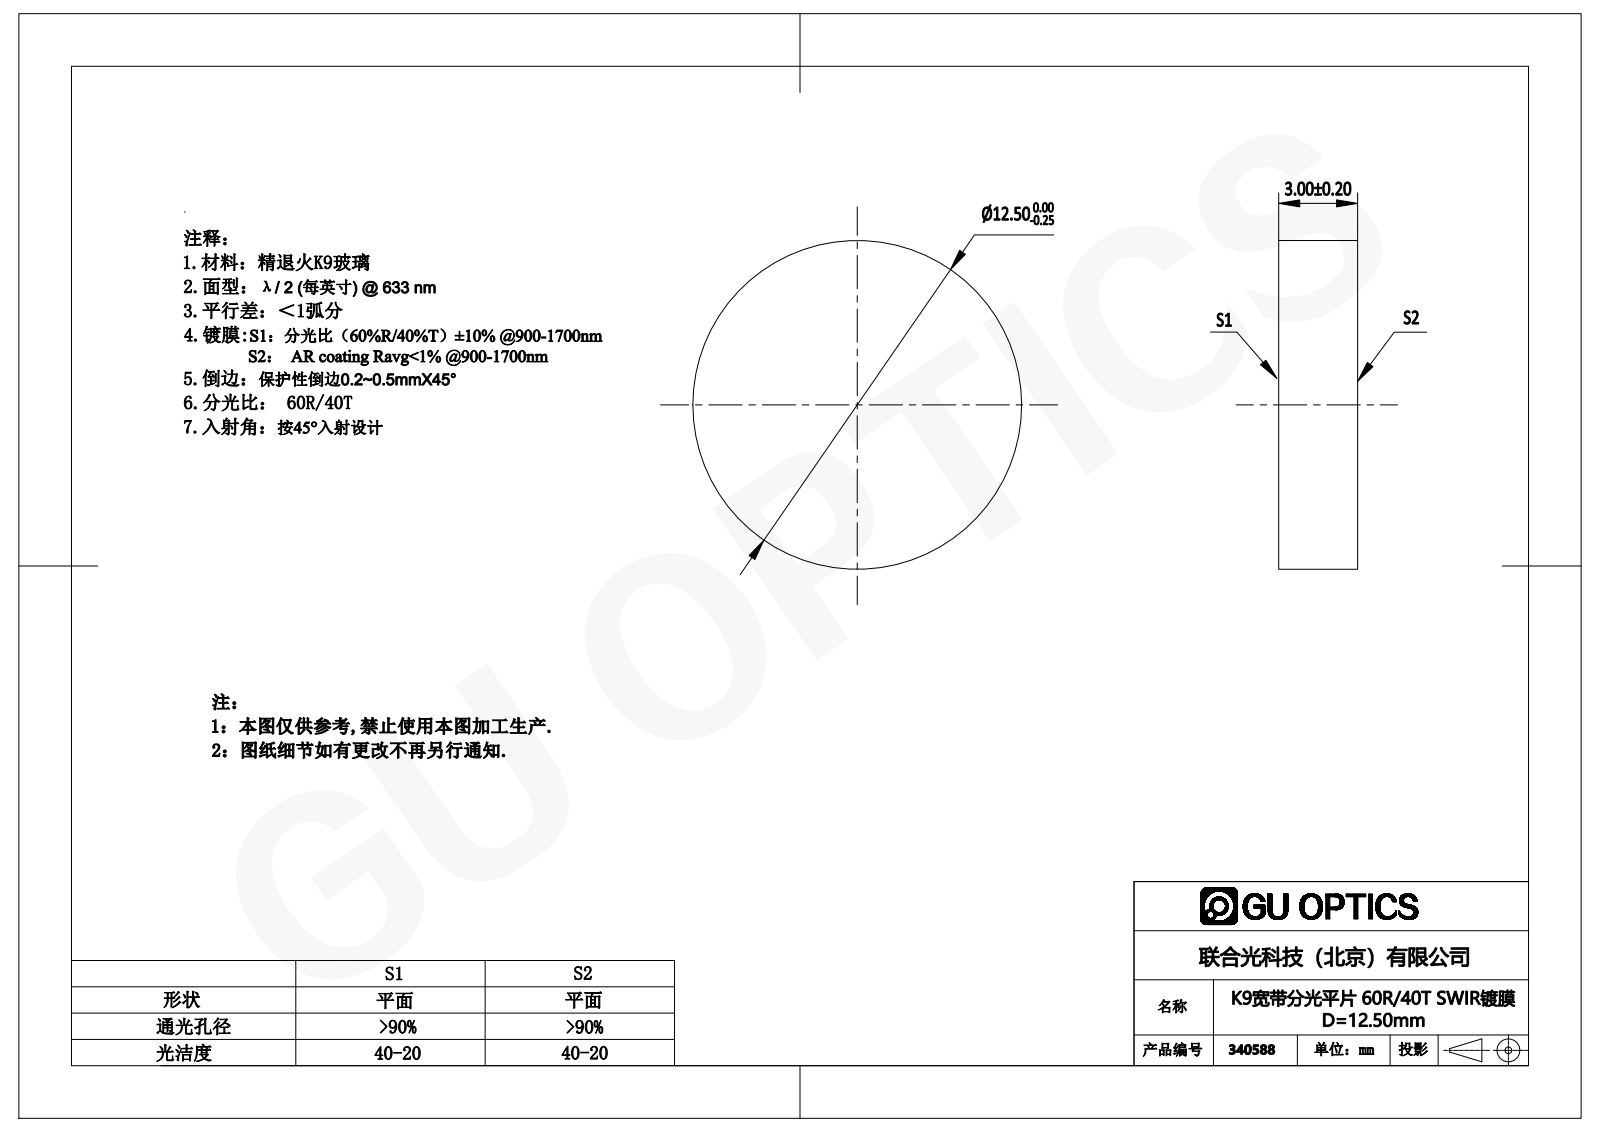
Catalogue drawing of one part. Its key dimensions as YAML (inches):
part_name: "340500"
step_written_by: "SolidWorks 2016 (CONFIG_CONTROL_DESIGN)"
units: inches
bodies: {solids: 1, faces: 4, planar: 2, cylindrical: 2, other: 0}
overall_size: [0.492, 0.492, 0.118]
volume: 0.022
surface_area: 0.563
round_bosses_or_shafts:
  - {diameter: 0.492, count: 1}
face_to_face_distances: [0.118]
